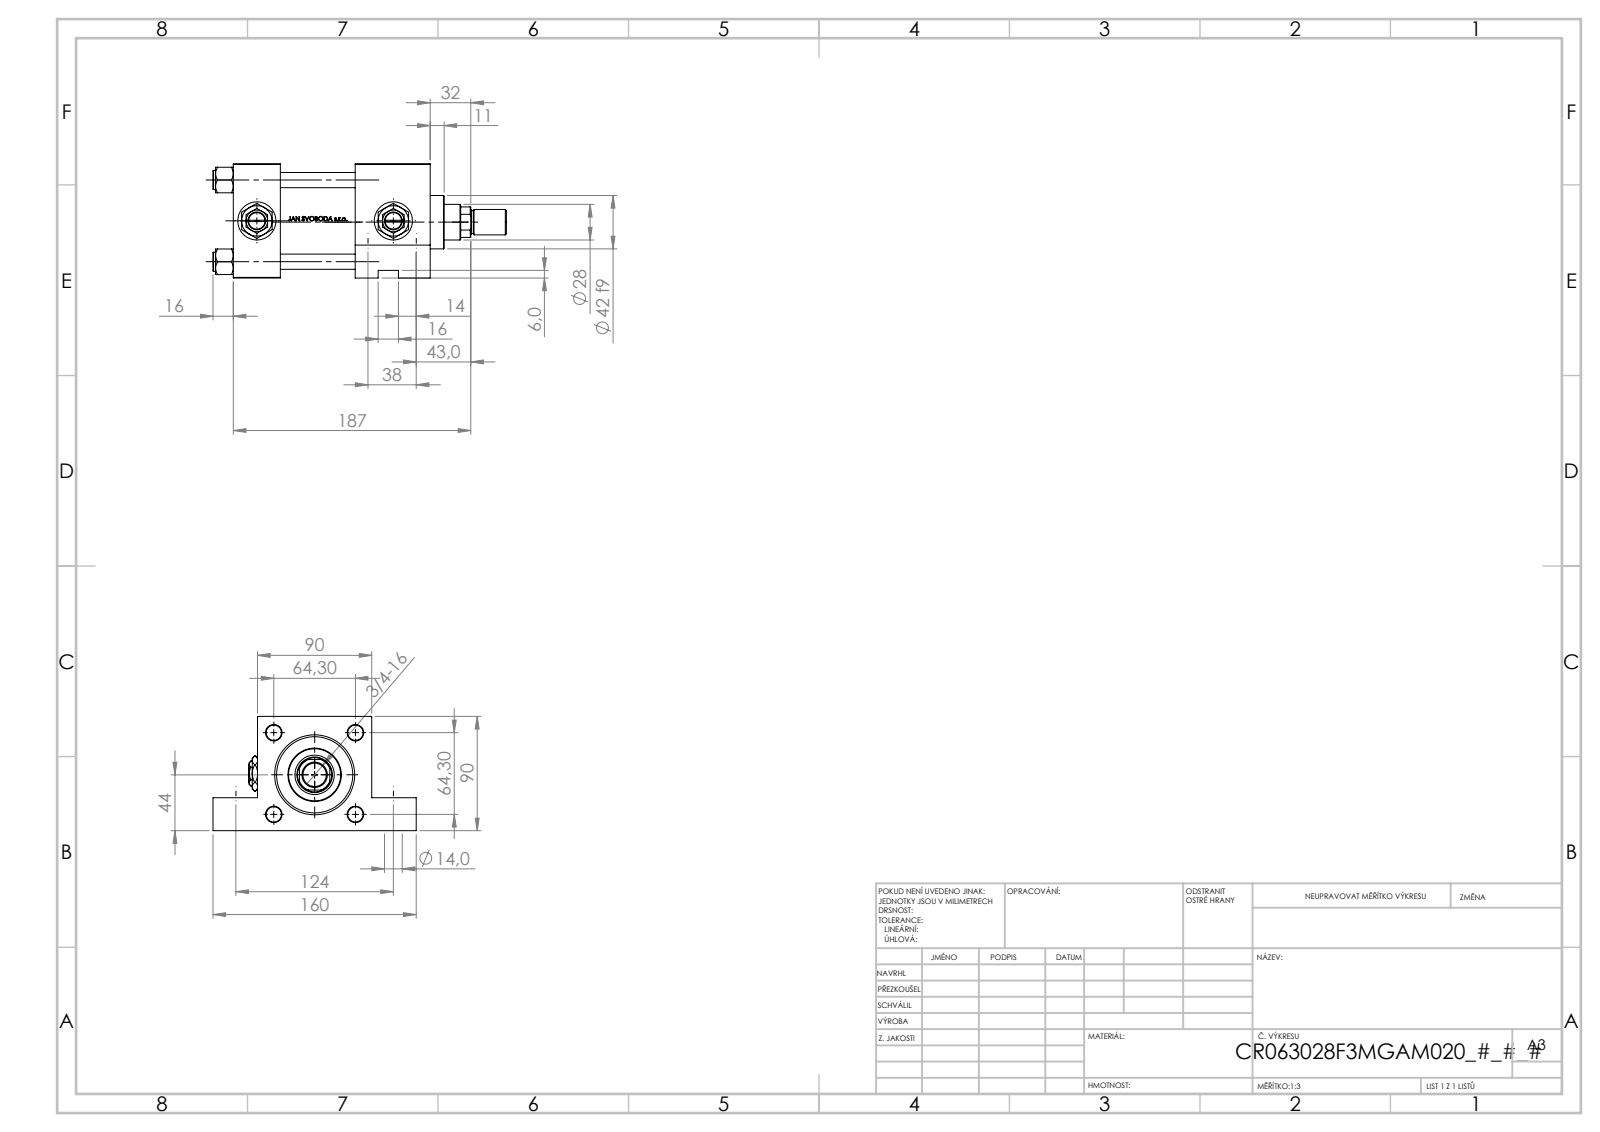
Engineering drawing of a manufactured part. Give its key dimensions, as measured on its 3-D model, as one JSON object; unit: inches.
{"part_name": "Zatka_pro_OIL_PORT; NUT_M5_F; V215CR_F_Body; V215CR_VCP_F (+3 more)", "step_written_by": "SolidWorks 2019 (CONFIG_CONTROL_DESIGN)", "units": "inches", "bodies": {"solids": 14, "faces": 1231, "planar": 492, "cylindrical": 151, "other": 588}, "overall_size": [9.094, 6.299, 3.543], "volume_in3": 62.31, "surface_area_in2": 312.2, "round_holes": [[0.472, 4], [0.709, 4], [0.825, 4], [1.181, 4], [0.276, 3], [0.098, 2], [0.728, 1], [1.102, 1], [1.22, 1], [1.969, 1], [2.362, 1], [2.48, 1]], "round_bosses_or_shafts": [[0.591, 4], [2.717, 1], [1.654, 1], [0.787, 1], [0.709, 1]], "partial_cylinders_radius": [[0.531, 1]], "face_to_face_distances": [3.543, 2.323, 1.457, 6.102, 4.646, 3.78, 0.787, 4.921, 2.52, 1.024], "hole_center_spacings": [1.275, 1.79, 2.531, 2.694, 1.112, 1.496, 2.469, 2.687]}
